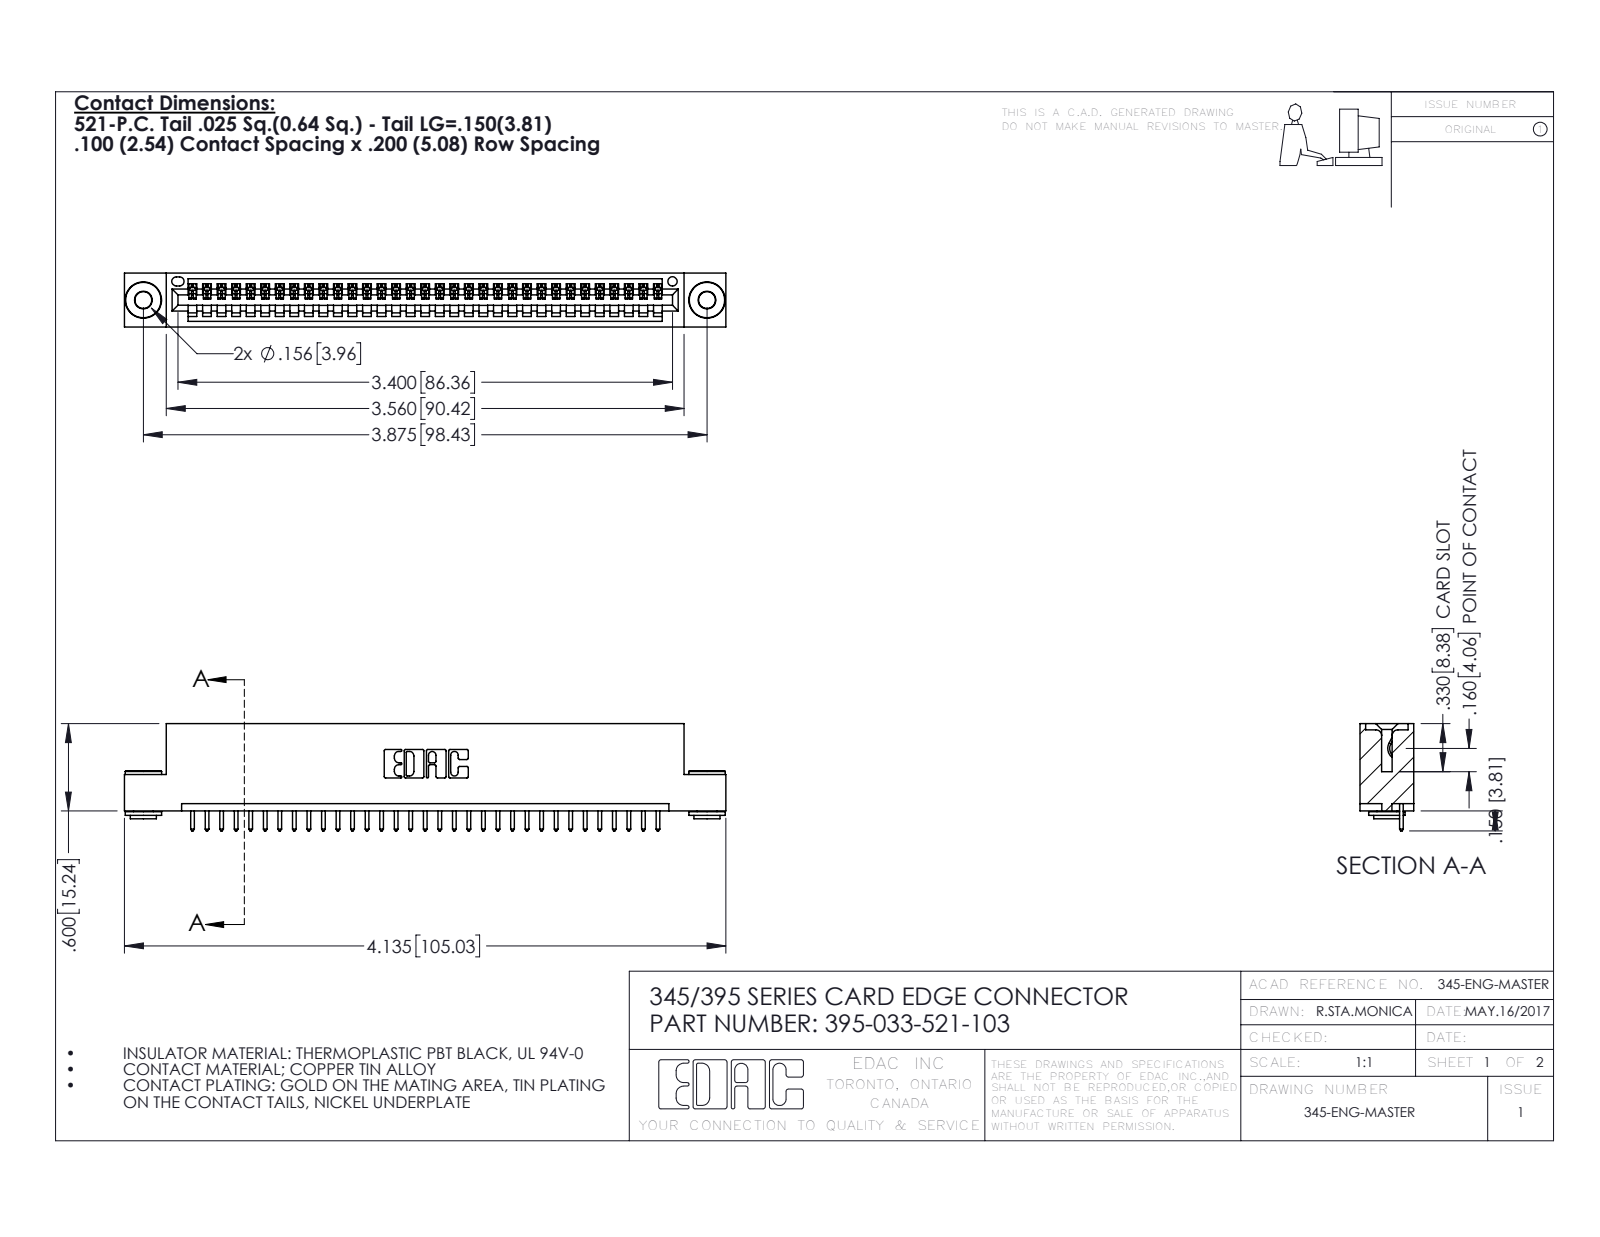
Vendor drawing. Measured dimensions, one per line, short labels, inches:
name: 395-033-521-103; 345 Part_Flush Mounting Lugs - 0.156 Dia-TH; 345-292-001_345-293-121; 345-250-002_345-250-002-102
written by: SolidWorks 2016 (CONFIG_CONTROL_DESIGN)
unit: in
bodies: 36 solids, 2078 faces (1410 planar, 660 cylindrical, 8 other)
size: 4.135 × 0.737 × 0.37
volume: 0.6 in³; area: 19.82 in²
holes: 2× ⌀0.116, 2× ⌀0.156, 1× ⌀0.064
bosses: 2× ⌀0.25, 2× ⌀0.18, 2× ⌀0.136
rounds: 66× R0.006, 66× R0.01, 22× R0.01, 6× R0.007, 6× R0.031, 3× R0.026, 2× R0.031, 2× R0.04
face distances: 0.072, 0.298, 0.2, 0.37, 0.025, 0.098, 0.272, 0.225, 0.149, 0.072
hole spacings: 0.27, 3.64, 3.875
